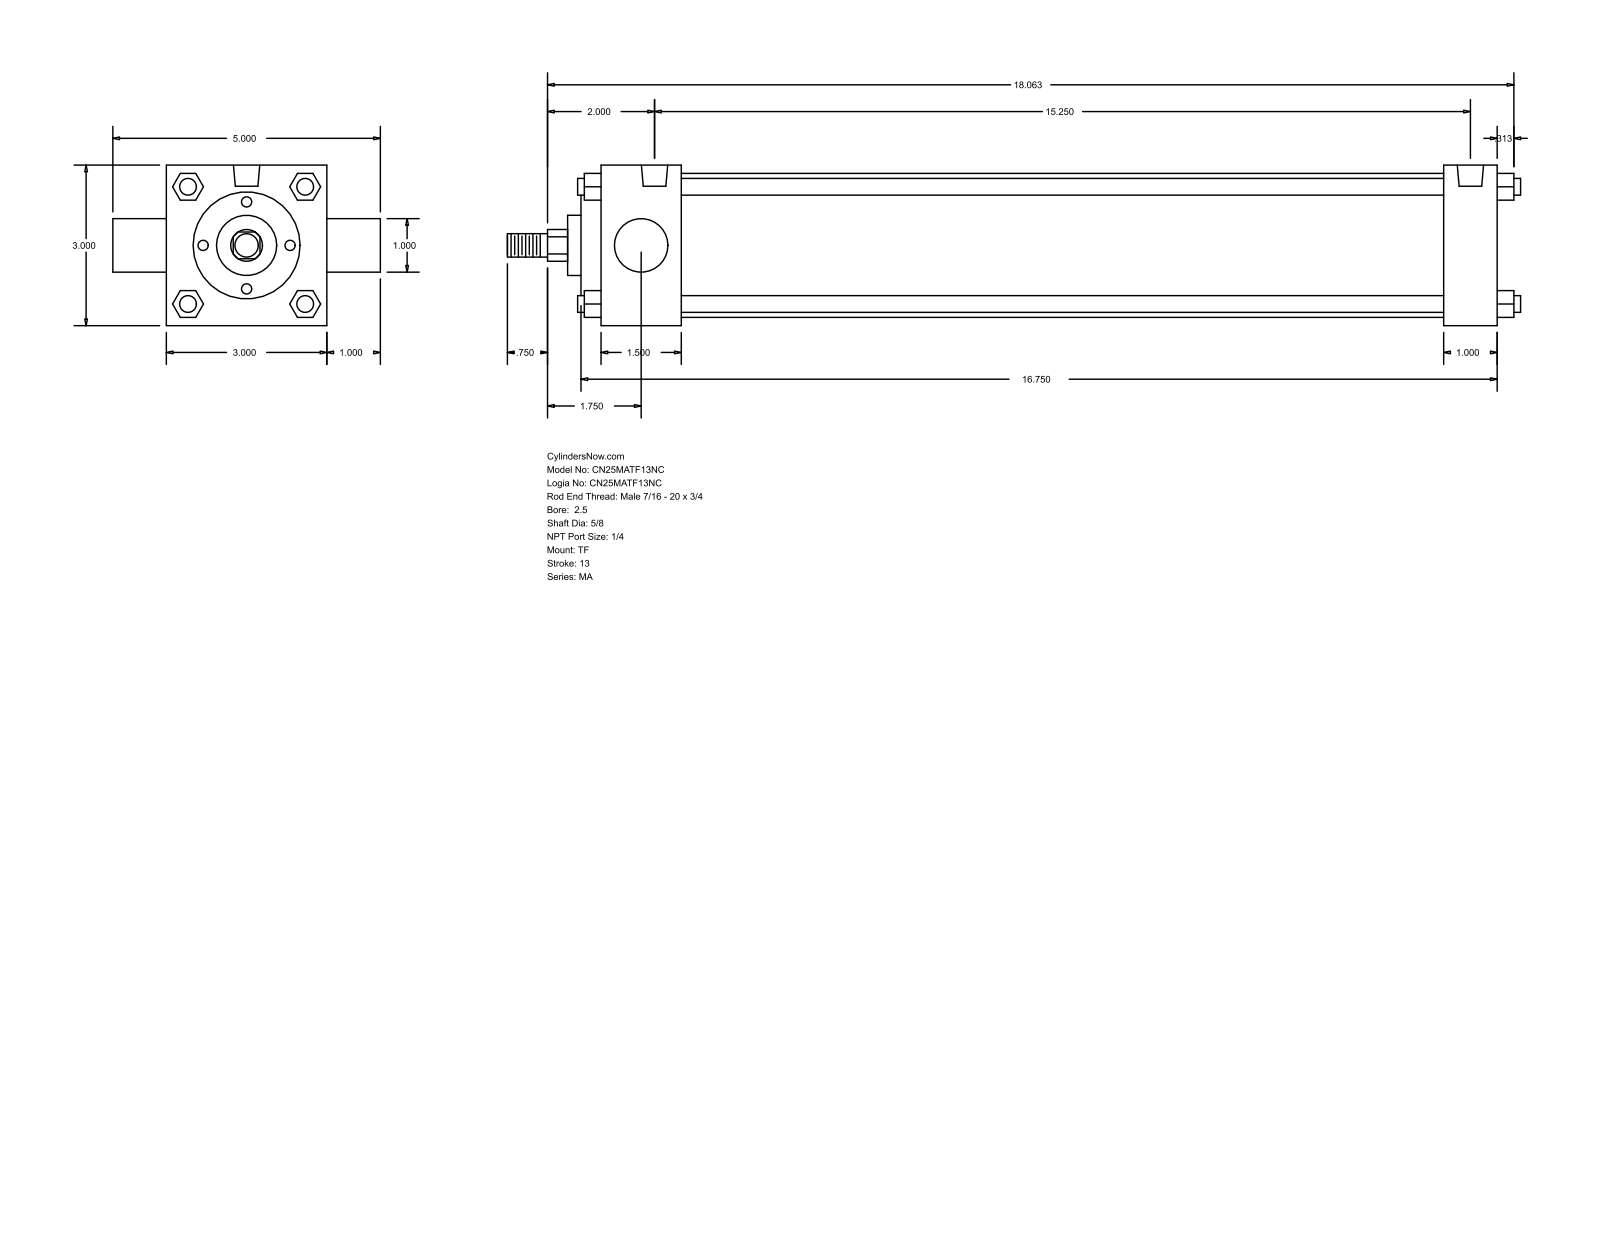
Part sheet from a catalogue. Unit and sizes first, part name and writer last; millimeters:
Units: millimetres
Overall size (bounding box): 481.01 × 127 × 76.2
Round holes (diameter × count): ⌀7.94 ×3, ⌀12.49 ×2
Round bosses / shafts (diameter × count): ⌀7.94 ×4, ⌀68.33 ×1, ⌀50.8 ×1, ⌀28.57 ×1, ⌀25.4 ×1, ⌀15.88 ×1, ⌀11.11 ×1
Partial cylindrical surfaces — rounded edges, fillets, slot ends (radius × count): R7.54 ×1
Main face-to-face distances: 76.2, 425.45, 25.4, 38.1, 400.05, 361.95, 387.35, 12.7, 9.52, 47.62
Hole centre spacings: 387.35
Bodies: 0 solids, 122 faces (93 planar, 29 cylindrical, 0 other)
Part name (STEP PRODUCT): MA_TF__0250_0.625
STEP written by: GSSL Pune (CONFIG_CONTROL_DESIGN)
